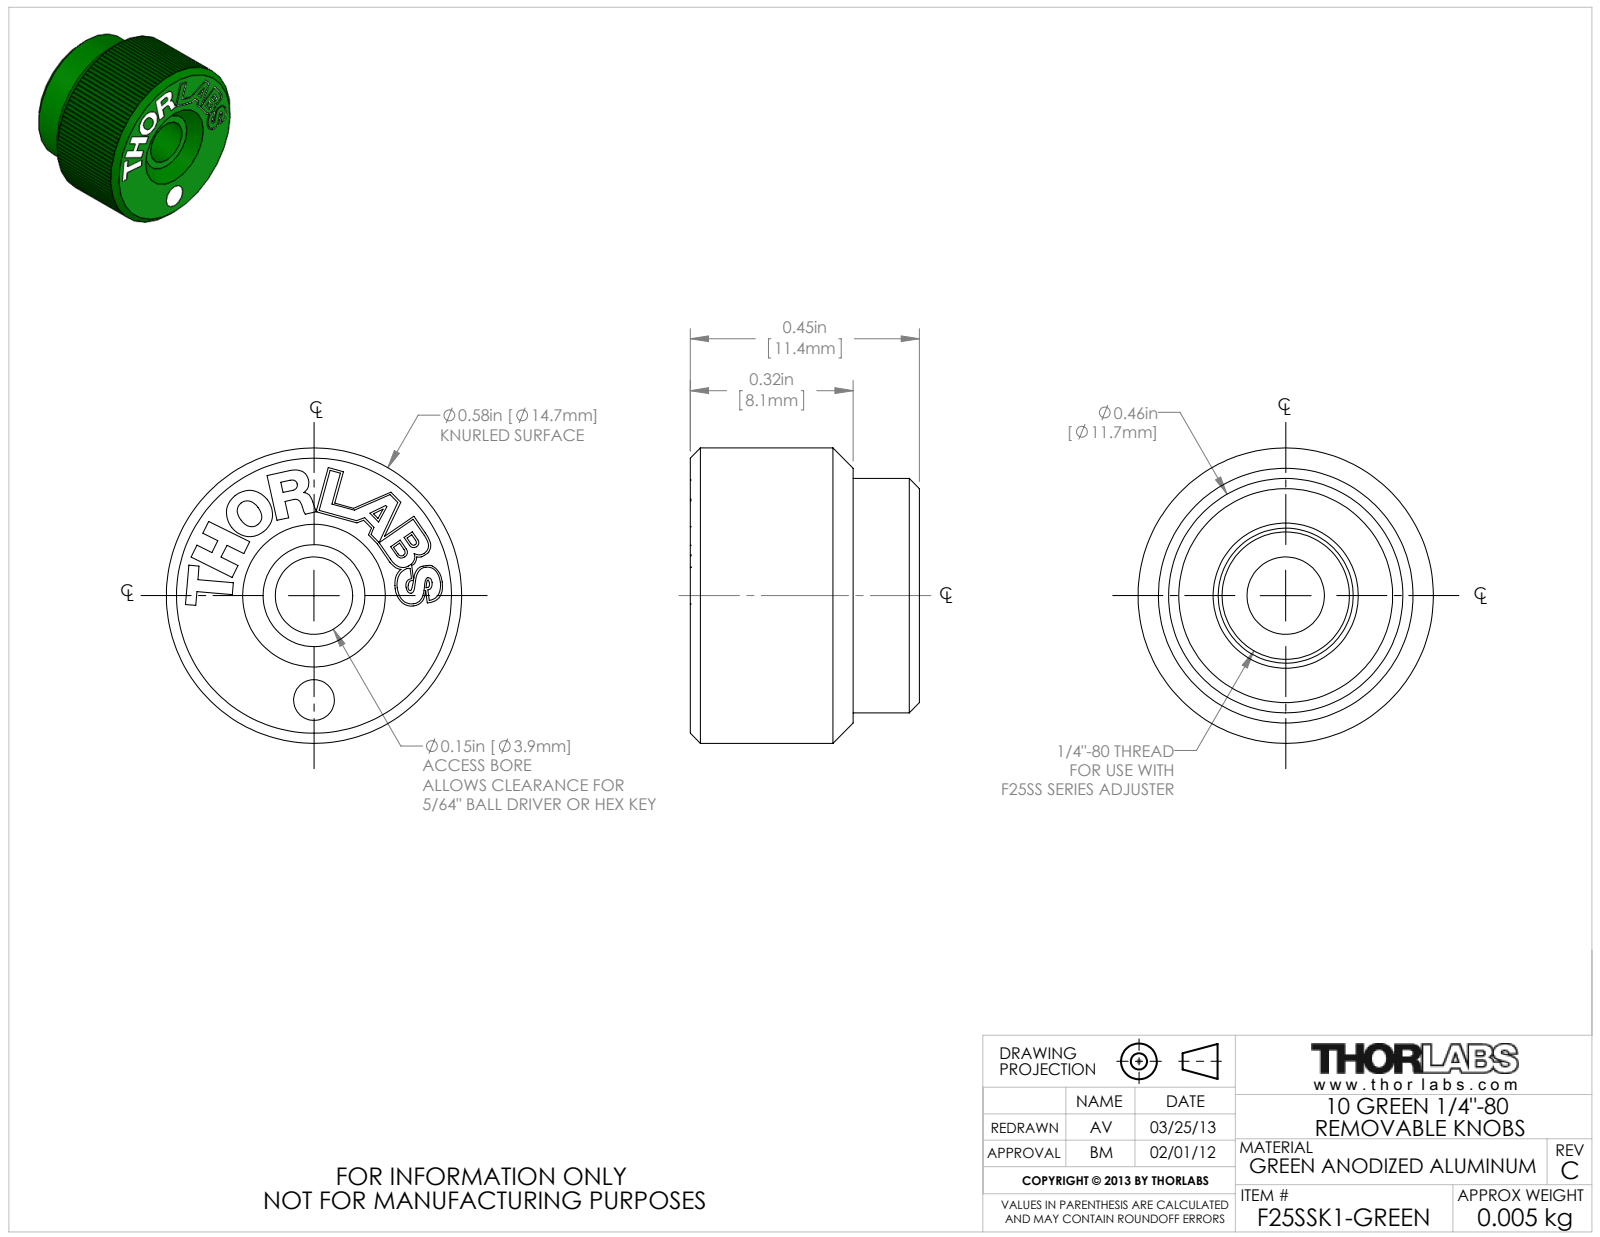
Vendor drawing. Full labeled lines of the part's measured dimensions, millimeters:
Part name (STEP PRODUCT): 23390-E0W
STEP written by: SolidWorks 2012 (AUTOMOTIVE_DESIGN)
Units: millimetres
Bodies: 1 solid, 210 faces (118 planar, 21 cylindrical, 71 other)
Overall size (bounding box): 14.7 × 14.7 × 11.4
Volume: 1 400 mm³ · Surface area: 953 mm²
Round holes (diameter × count): ⌀2 ×1, ⌀3.9 ×1, ⌀6.4 ×1, ⌀6.7 ×1, ⌀7.4 ×1
Round bosses / shafts (diameter × count): ⌀14.7 ×1, ⌀11.7 ×1
Partial cylindrical surfaces — rounded edges, fillets, slot ends (radius × count): R0.4 ×1, R1.2 ×1, R1.5 ×1
Main face-to-face distances: 11.4, 6.9, 4.6, 8.1, 1.3, 3.3, 6.9, 8.1, 11.4, 0.5
Hole centre spacings: 5.2
